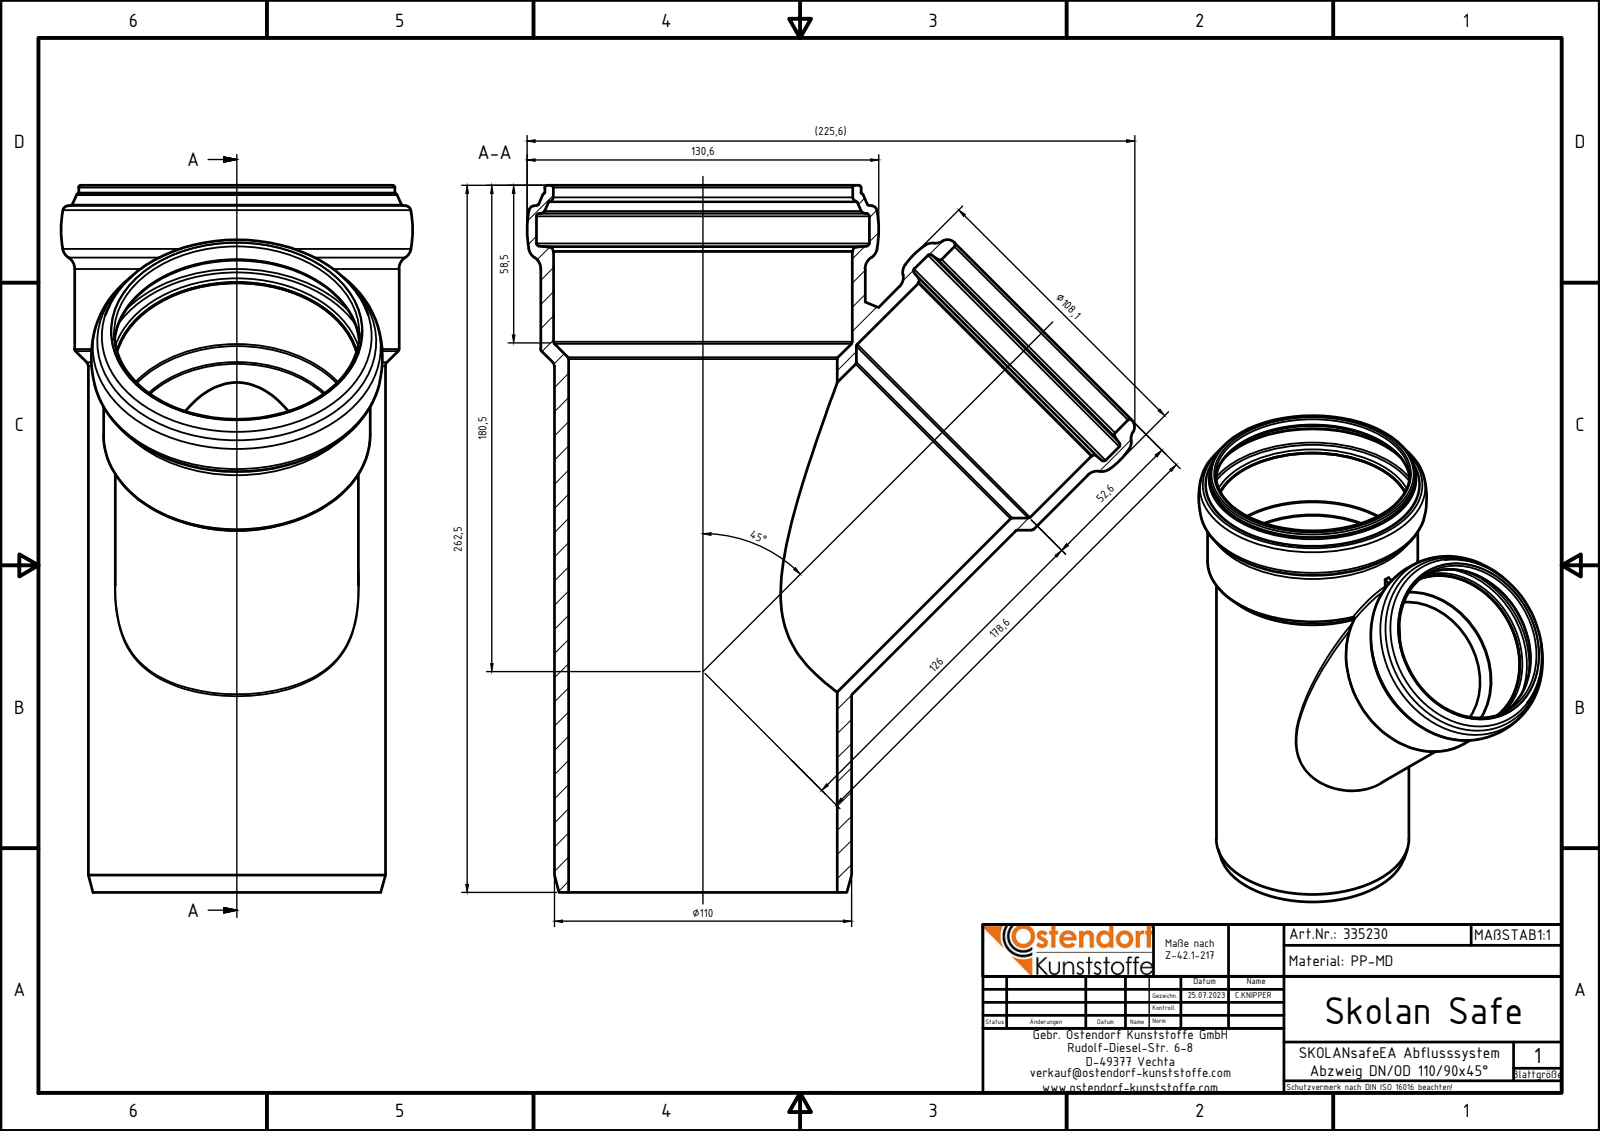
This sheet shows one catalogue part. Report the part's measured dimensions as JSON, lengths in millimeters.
{"part_name": "335230z", "step_written_by": "Autodesk Inventor 2020 (AUTOMOTIVE_DESIGN)", "units": "millimeters", "bodies": {"solids": 1, "faces": 95, "planar": 8, "cylindrical": 15, "other": 72}, "overall_size": [262.5, 225.61, 130.6], "volume_mm3": 567154, "surface_area_mm2": 240171, "round_holes": [[81.3, 1], [90.8, 1], [91.1, 1], [99.7, 1], [100.5, 1], [110.9, 1], [111.2, 1], [123.6, 1]], "round_bosses_or_shafts": [[120.5, 1], [117.4, 1], [110.3, 1], [99, 1], [90.3, 1]], "face_to_face_distances": [262.5, 238, 24.5, 20, 3]}
